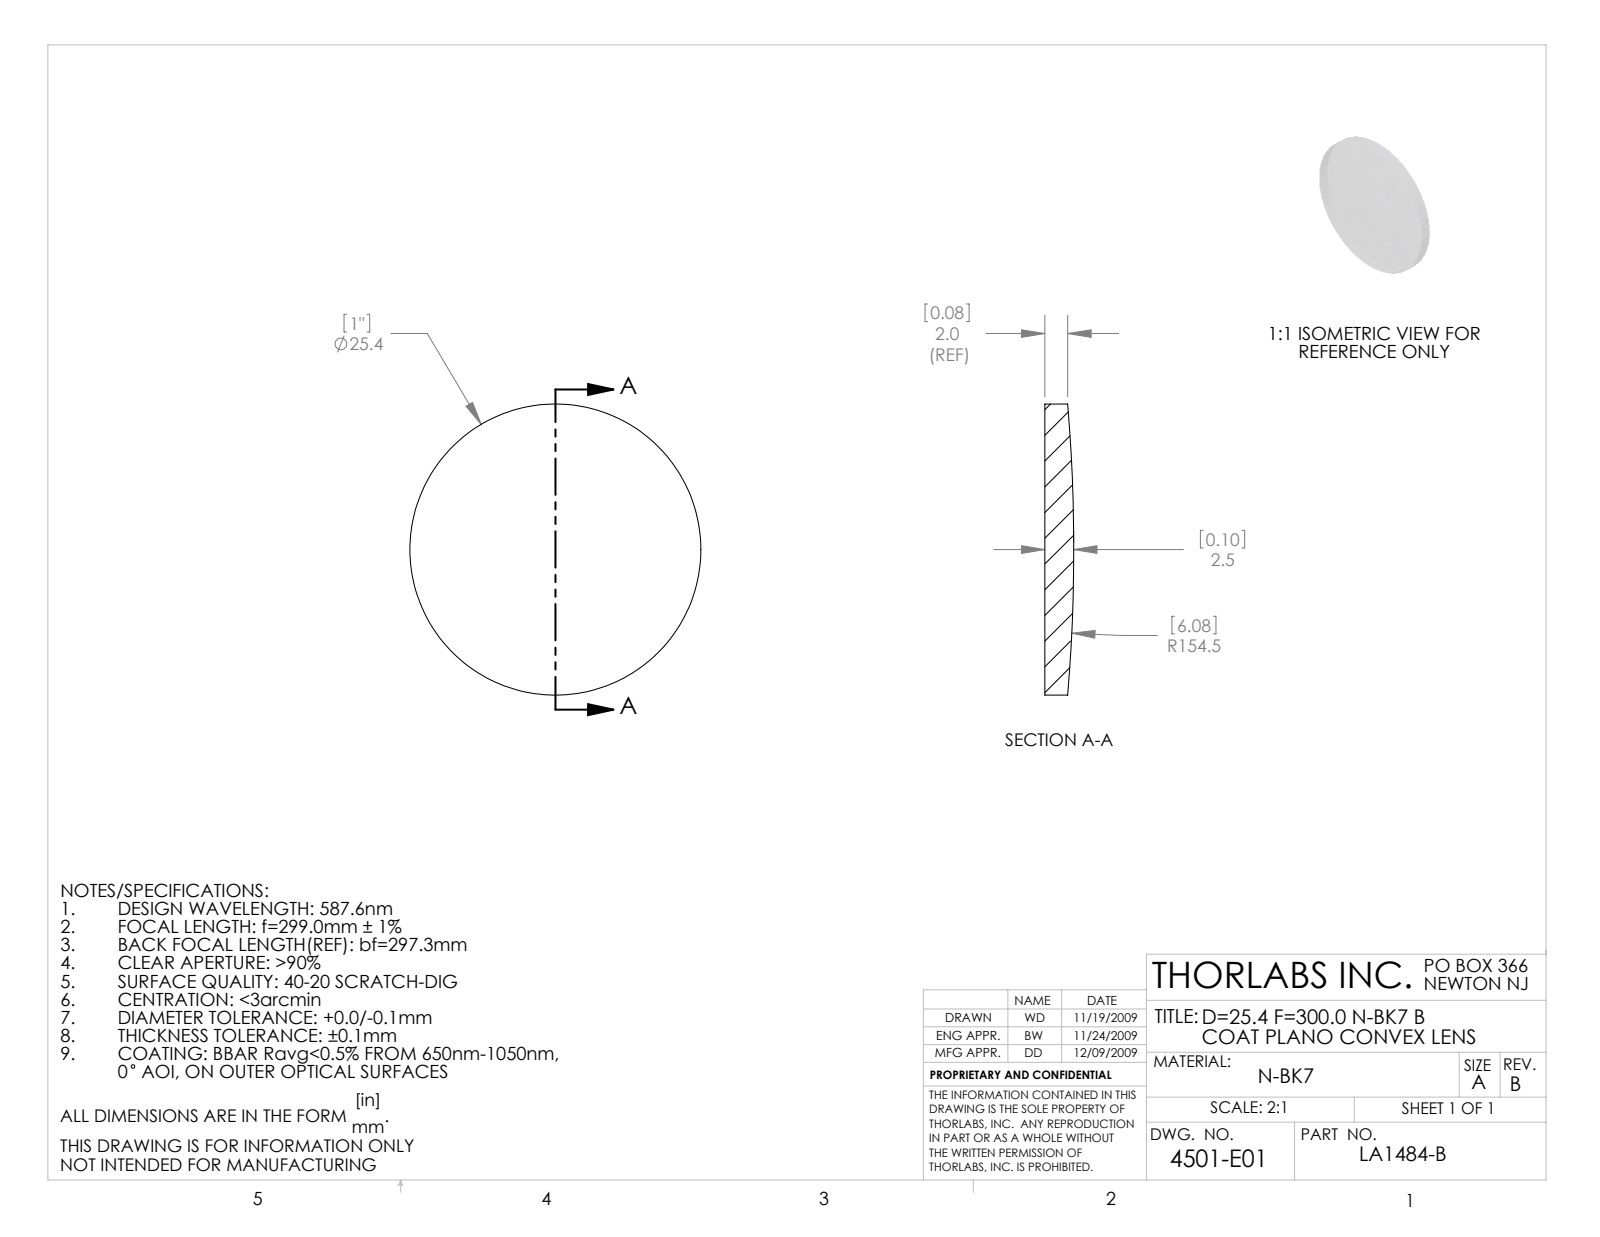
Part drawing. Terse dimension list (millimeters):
name: 4501-E0W
written by: SolidWorks 2009 (AUTOMOTIVE_DESIGN)
unit: mm
bodies: 1 solid, 5 faces (1 planar, 2 cylindrical, 2 other)
size: 25.4 × 25.4 × 2.52
volume: 1 145 mm³; area: 1 174 mm²
bosses: 1× ⌀25.4
